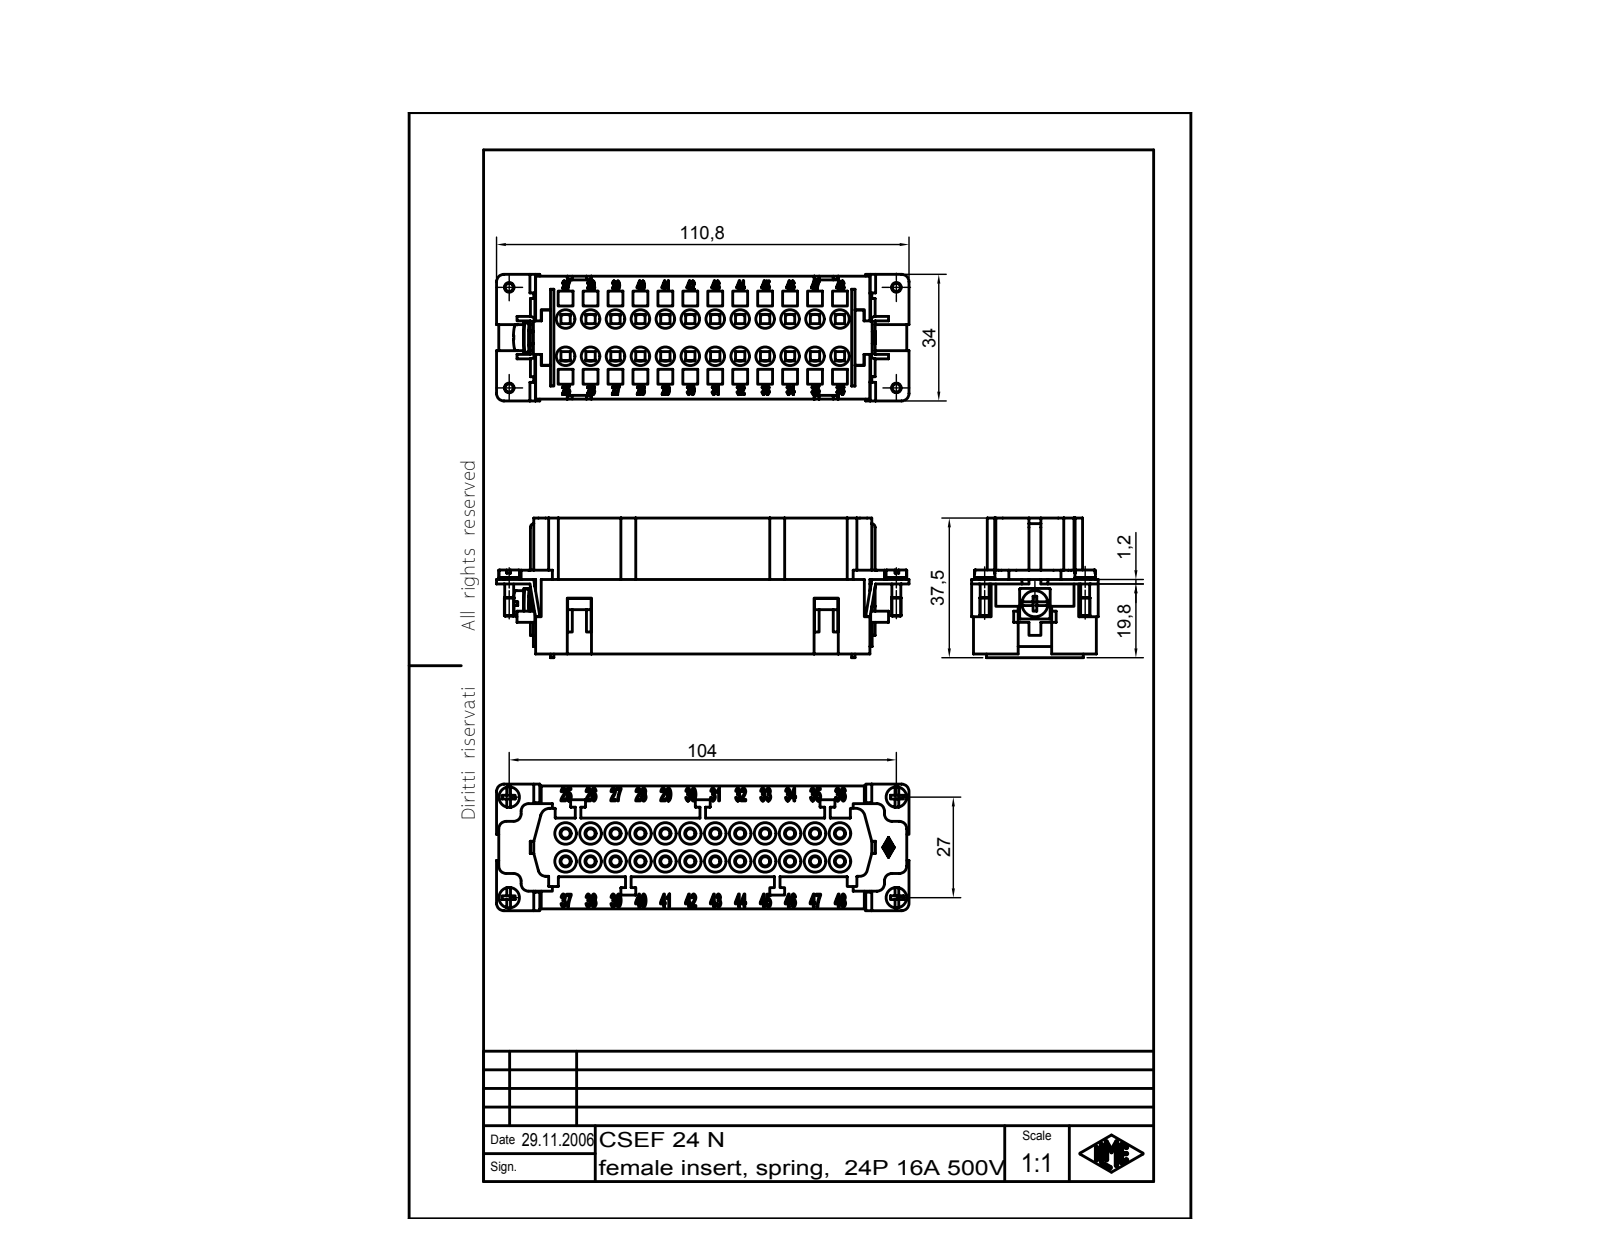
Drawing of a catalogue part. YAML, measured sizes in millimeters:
part_name: "CSEF Kontakteinsätze mit Käfigzugfederanschluss"
step_written_by: "Autodesk Inventor 7 (AUTOMOTIVE_DESIGN)"
units: millimeters
bodies: {solids: 1, faces: 2837, planar: 1139, cylindrical: 252, other: 1446}
overall_size: [110.8, 37.5, 34]
volume: 75544
surface_area: 32029
round_holes:
  - {diameter: 5, count: 24}
  - {diameter: 2.5, count: 12}
  - {diameter: 3, count: 12}
  - {diameter: 5.8, count: 12}
  - {diameter: 3.24, count: 1}
round_bosses_or_shafts:
  - {diameter: 5.5, count: 2}
  - {diameter: 5.4, count: 2}
  - {diameter: 2.6, count: 2}
  - {diameter: 2.4, count: 2}
  - {diameter: 7, count: 1}
  - {diameter: 4, count: 1}
partial_cylinders:
  - {radius: 0.1, count: 22}
  - {radius: 2, count: 17}
  - {radius: 0.1, count: 14}
  - {radius: 1, count: 2}
  - {radius: 1.25, count: 2}
  - {radius: 2.5, count: 1}
  - {radius: 5.66, count: 1}
face_to_face_distances: [8.62, 24.38, 20, 33, 4, 15.76, 36.5, 16.5, 10, 8]
hole_center_spacings: [6.7, 6.82, 13.4, 13.46, 20.1, 20.14, 26.8, 26.83]
